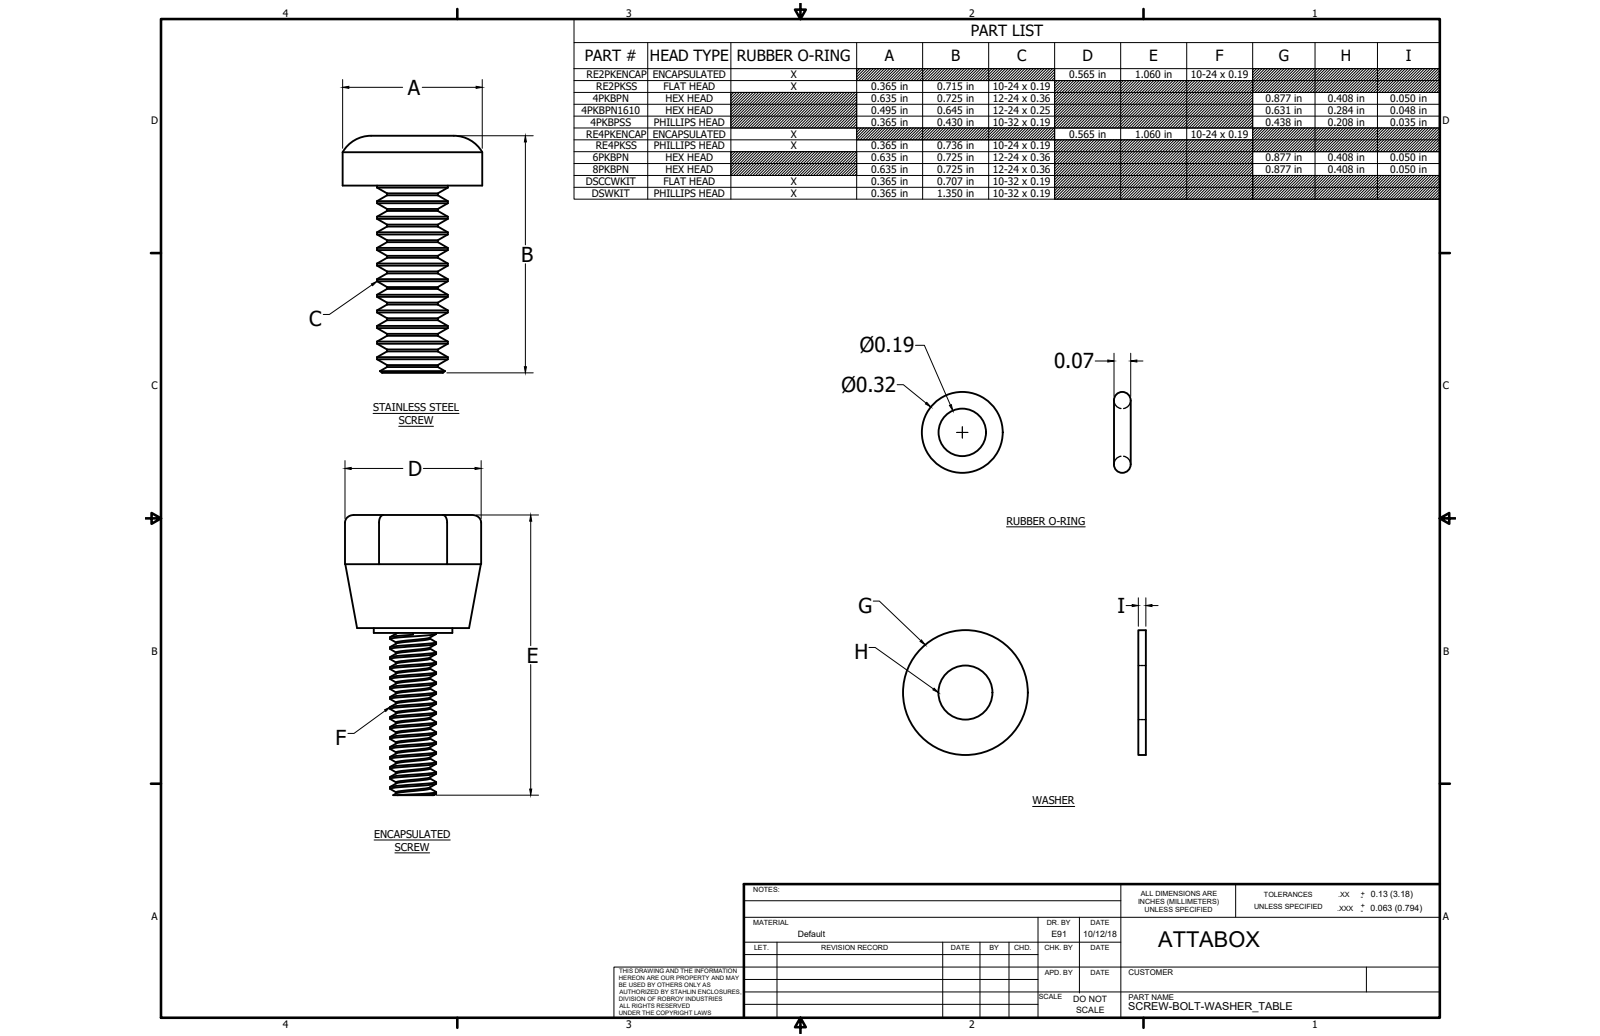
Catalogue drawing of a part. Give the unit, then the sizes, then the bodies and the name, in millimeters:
Units: millimetres
Overall size (bounding box): 90.1 × 28.5 × 13.8
Round holes (diameter × count): ⌀9.5 ×4
Round bosses / shafts (diameter × count): ⌀8 ×4, ⌀4.7 ×4
Partial cylindrical surfaces — rounded edges, fillets, slot ends (radius × count): R0.8 ×18
Main face-to-face distances: 12, 22, 44, 11.4, 0.5, 11.9, 22, 34, 56, 10
Hole centre spacings: 25.4, 50.8, 76.2
Volume: 6 950 mm³ · Surface area: 3 861 mm²
Bodies: 4 solids, 136 faces (92 planar, 36 cylindrical, 8 other)
Part name (STEP PRODUCT): RE4PKENCAP
STEP written by: SolidWorks 2017 (AUTOMOTIVE_DESIGN)
